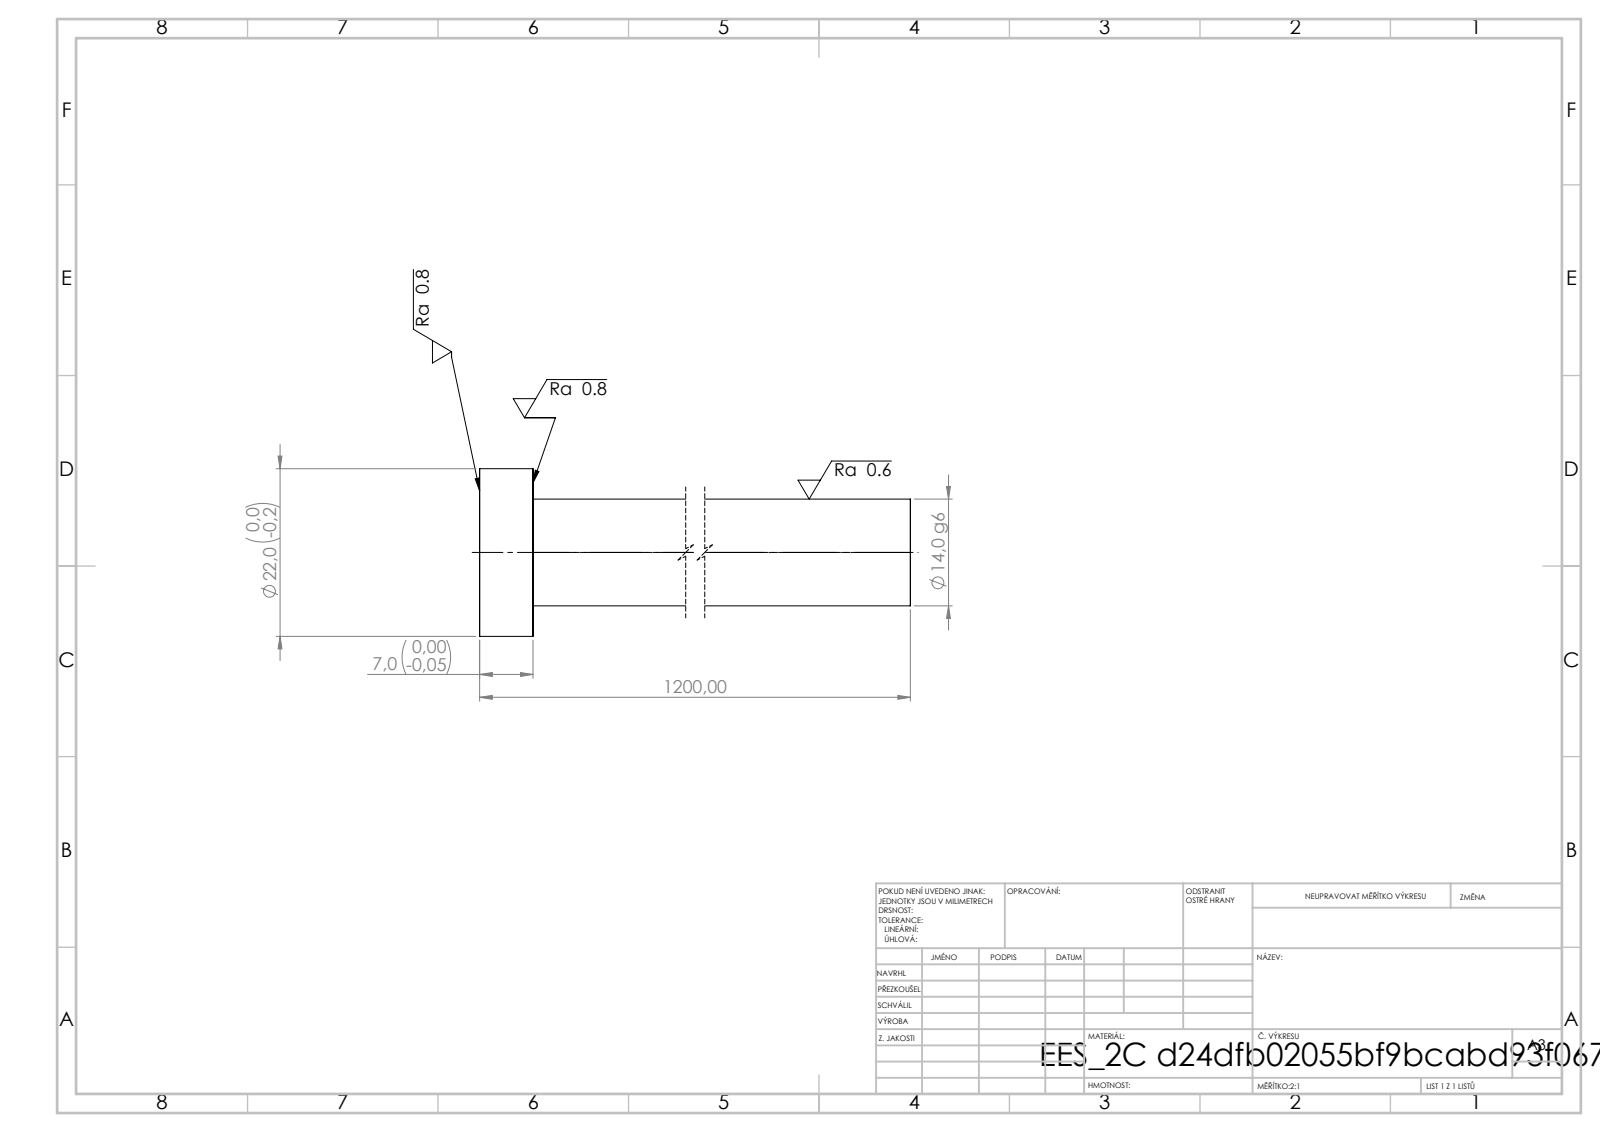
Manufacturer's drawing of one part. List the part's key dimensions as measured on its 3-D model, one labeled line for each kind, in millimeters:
STEP written by: SolidWorks 2019 (CONFIG_CONTROL_DESIGN)
Units: millimetres
Bodies: 1 solid, 7 faces (3 planar, 4 cylindrical, 0 other)
Overall size (bounding box): 1200 × 22 × 22
Volume: 186 309 mm³ · Surface area: 53 715 mm²
Round bosses / shafts (diameter × count): ⌀22 ×1, ⌀14 ×1
Main face-to-face distances: 7, 1200, 1193
